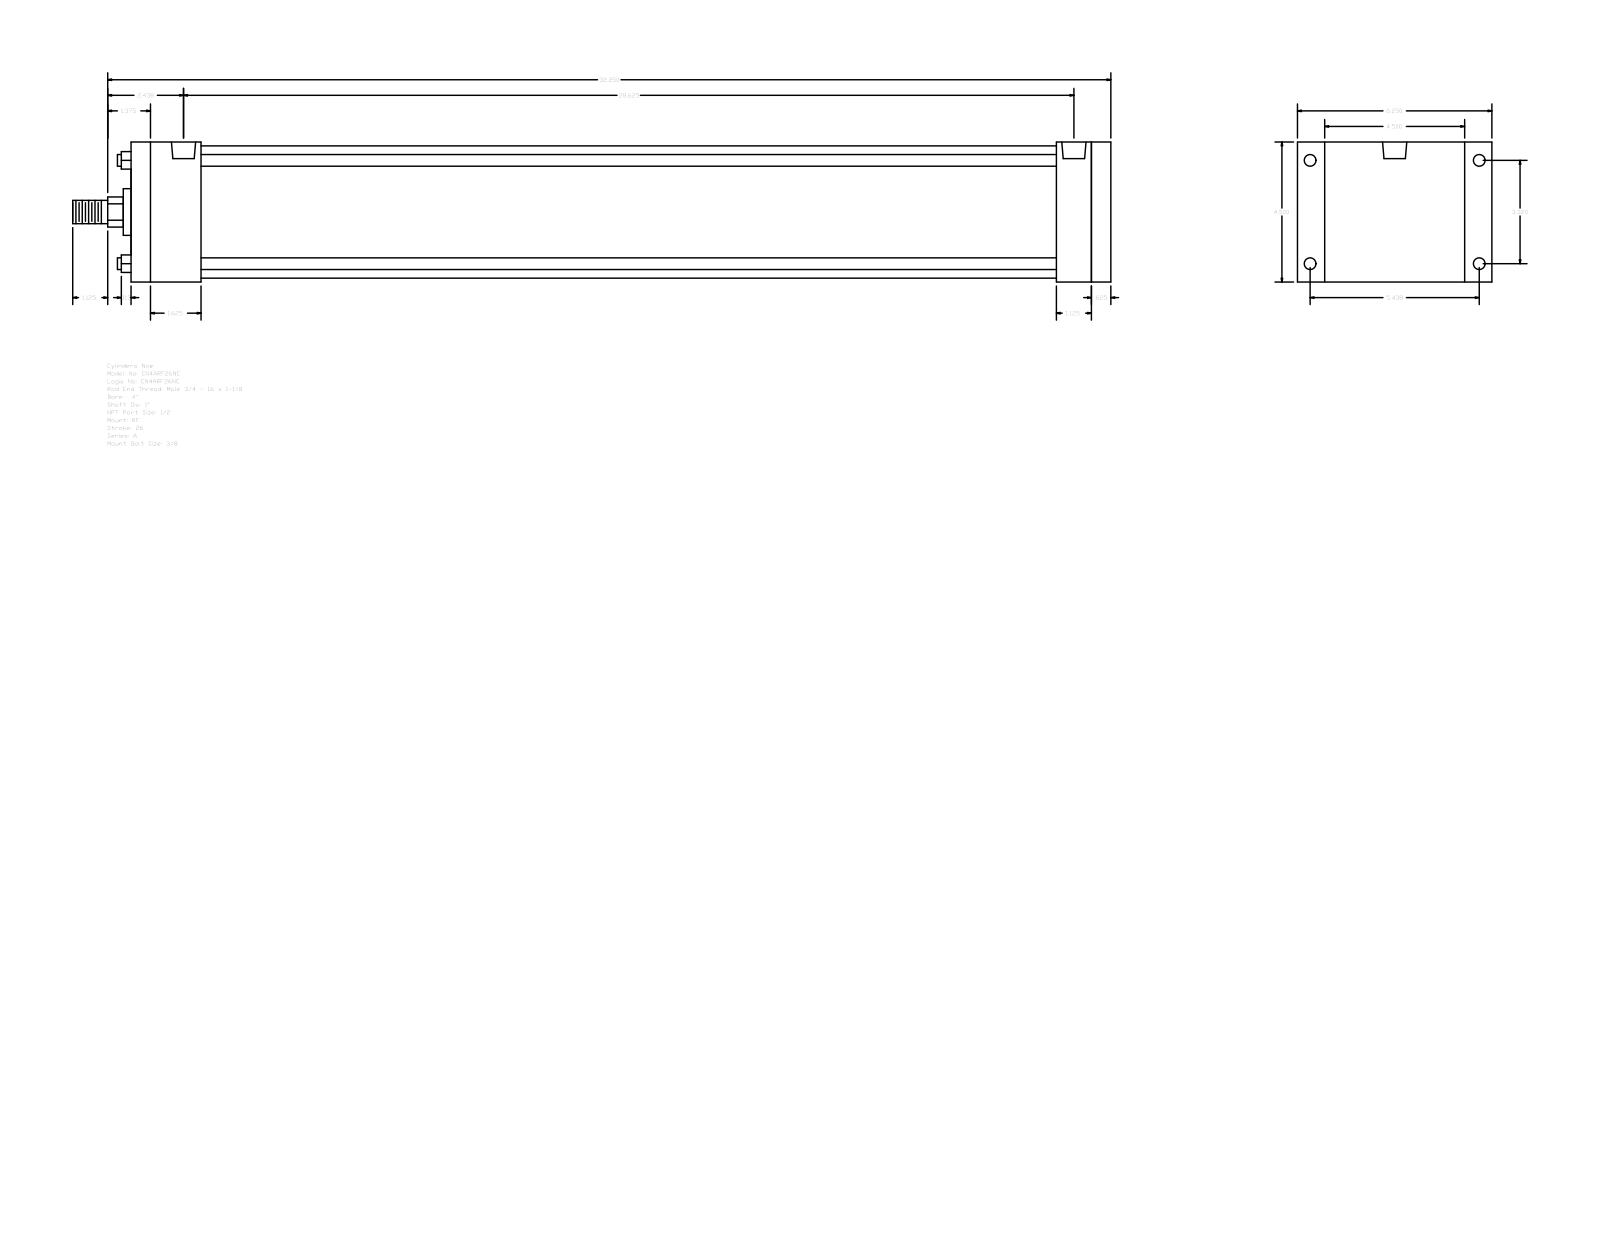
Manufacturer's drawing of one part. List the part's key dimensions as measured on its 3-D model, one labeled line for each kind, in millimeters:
Part name (STEP PRODUCT): A_RF__0400_1
STEP written by: GSSL Pune (CONFIG_CONTROL_DESIGN)
Units: millimetres
Bodies: 0 solids, 92 faces (64 planar, 28 cylindrical, 0 other)
Overall size (bounding box): 847.73 × 158.75 × 114.3
Round holes (diameter × count): ⌀8.73 ×4, ⌀9.53 ×4, ⌀19.77 ×2
Round bosses / shafts (diameter × count): ⌀9.53 ×4, ⌀107.95 ×1, ⌀38.1 ×1, ⌀25.4 ×1, ⌀19.05 ×1
Partial cylindrical surfaces — rounded edges, fillets, slot ends (radius × count): R12.29 ×1
Main face-to-face distances: 114.3, 800.1, 784.22, 15.88, 28.57, 22.23, 136.53, 755.65, 44.45, 57.15
Hole centre spacings: 3.18, 84.32, 138.12, 161.82, 720.72, 723.9, 727.08
